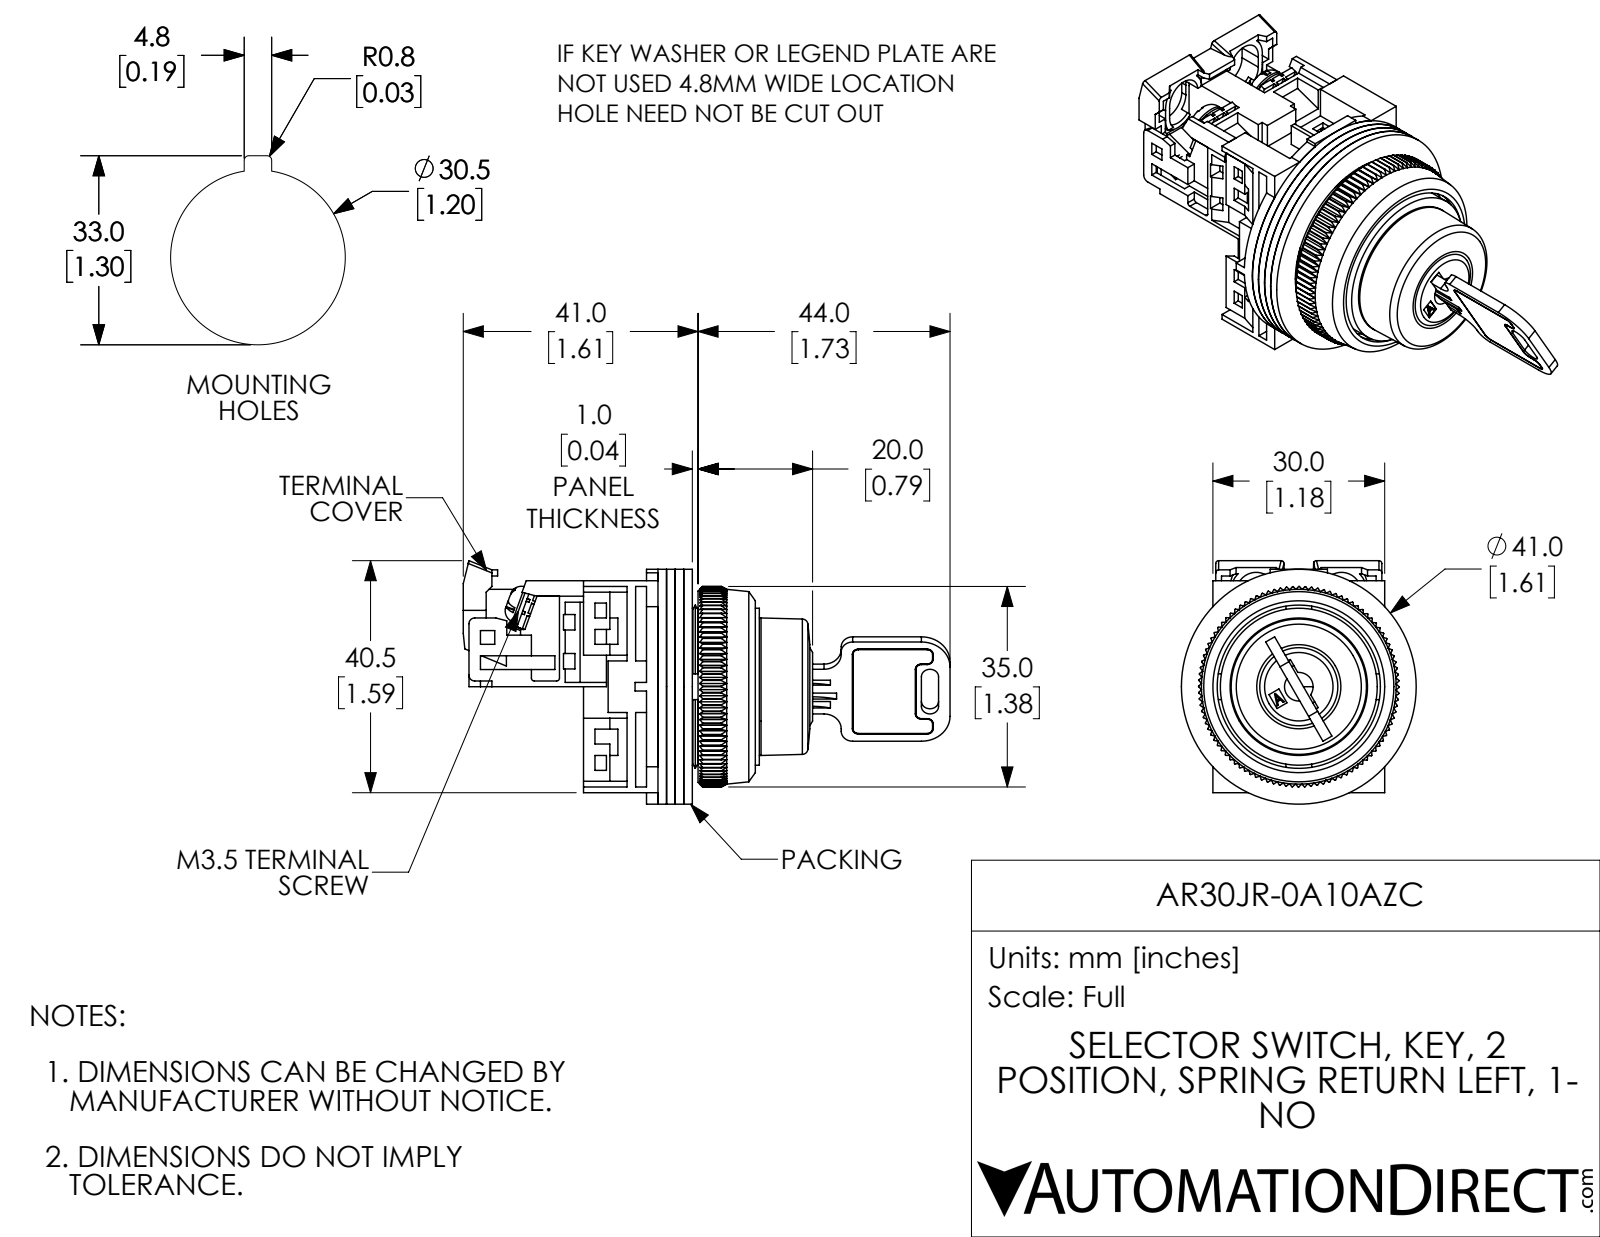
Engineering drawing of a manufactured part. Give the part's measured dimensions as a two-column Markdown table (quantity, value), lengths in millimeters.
| quantity | value |
| --- | --- |
| part name | AR30JR-0A10AZC |
| STEP written by | SolidWorks 2017 (AUTOMOTIVE_DESIGN) |
| units | millimeters |
| bodies | 16 solids, 1404 faces (938 planar, 218 cylindrical, 248 other) |
| overall size | 85 × 42.5 × 41 |
| volume | 32 180 mm³ |
| surface area | 29 280 mm² |
| round holes (diameter × count) | 3.5 × 4, 3.6 × 2, 3 × 1, 18 × 1, 24 × 1, 28.5 × 1, 30 × 1, 31.8 × 1 |
| round bosses / shafts (diameter × count) | 6.6 × 2, 3.5 × 2, 41 × 1, 29.2 × 1, 27.4 × 1 |
| partial cylindrical surfaces (radius × count) | 1.5 × 10, 0.5 × 6, 0.2 × 4, 1 × 3, 3 × 3, 2 × 2, 3.5 × 2, 4.5 × 2 |
| main face-to-face distances | 1.5, 3, 2, 1, 4.5, 5, 3.5, 6.5, 8, 17.5 |
| hole center spacings | 14.7, 15.5 |
